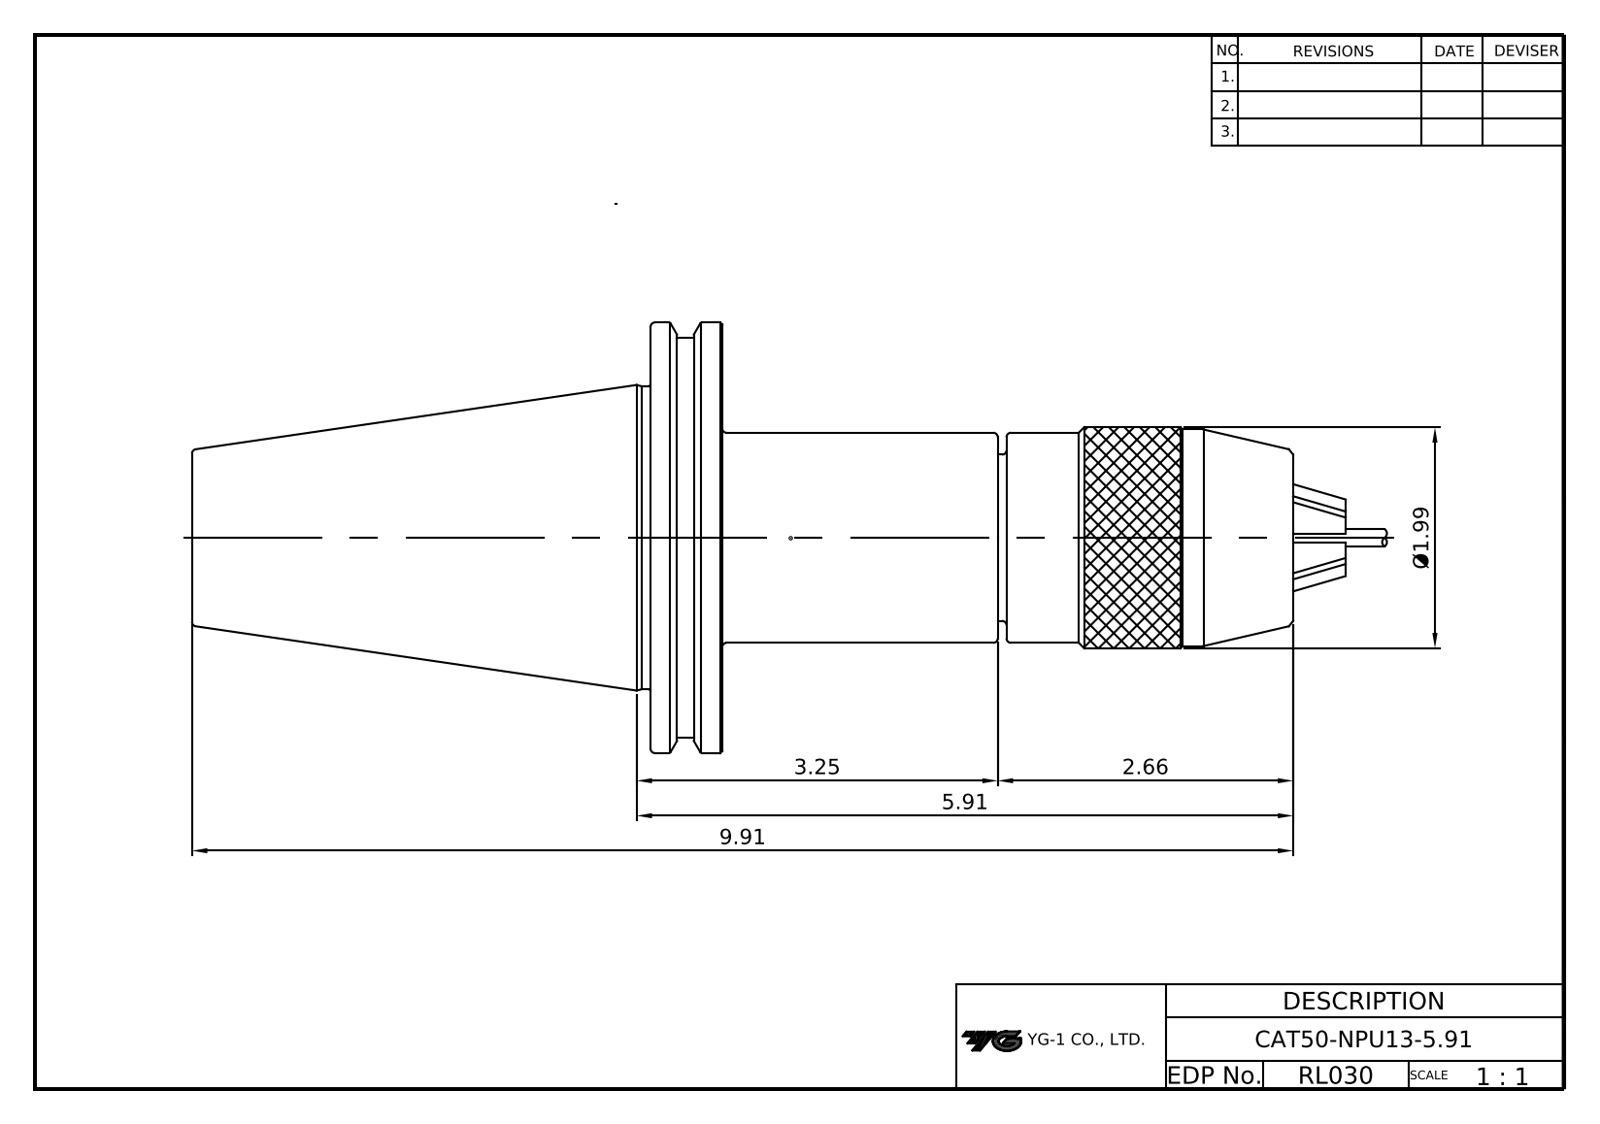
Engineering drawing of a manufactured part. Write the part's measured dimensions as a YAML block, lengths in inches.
part_name: "LO-CAT50-NPU13-150; NPU13; BB1271306M401A; BB12713070101A (+2 more)"
step_written_by: "Autodesk Inventor 2025 (AP242_MANAGED_MODEL_BASED_3D_ENGINEERING_MIM_LF)"
units: inches
bodies: {solids: 7, faces: 217, planar: 144, cylindrical: 40, other: 33}
overall_size: [10.359, 3.875, 3.728]
volume: 33.71
surface_area: 129.4
round_holes:
  - {diameter: 0.354, count: 1}
  - {diameter: 0.375, count: 1}
  - {diameter: 0.551, count: 1}
  - {diameter: 0.865, count: 1}
  - {diameter: 0.925, count: 1}
  - {diameter: 1.031, count: 1}
  - {diameter: 1.516, count: 1}
  - {diameter: 1.732, count: 1}
round_bosses_or_shafts:
  - {diameter: 3.875, count: 1}
  - {diameter: 3.594, count: 1}
  - {diameter: 2.726, count: 1}
  - {diameter: 1.969, count: 1}
  - {diameter: 1.945, count: 1}
  - {diameter: 1.89, count: 1}
  - {diameter: 1.654, count: 1}
  - {diameter: 1.496, count: 1}
partial_cylinders:
  - {radius: 0.012, count: 6}
  - {radius: 0.098, count: 6}
  - {radius: 0.039, count: 3}
  - {radius: 0.354, count: 3}
face_to_face_distances: [3.226, 3.852, 0.625, 2.611, 1.986, 1.24, 0.098, 5.781, 5.156, 3.169]
